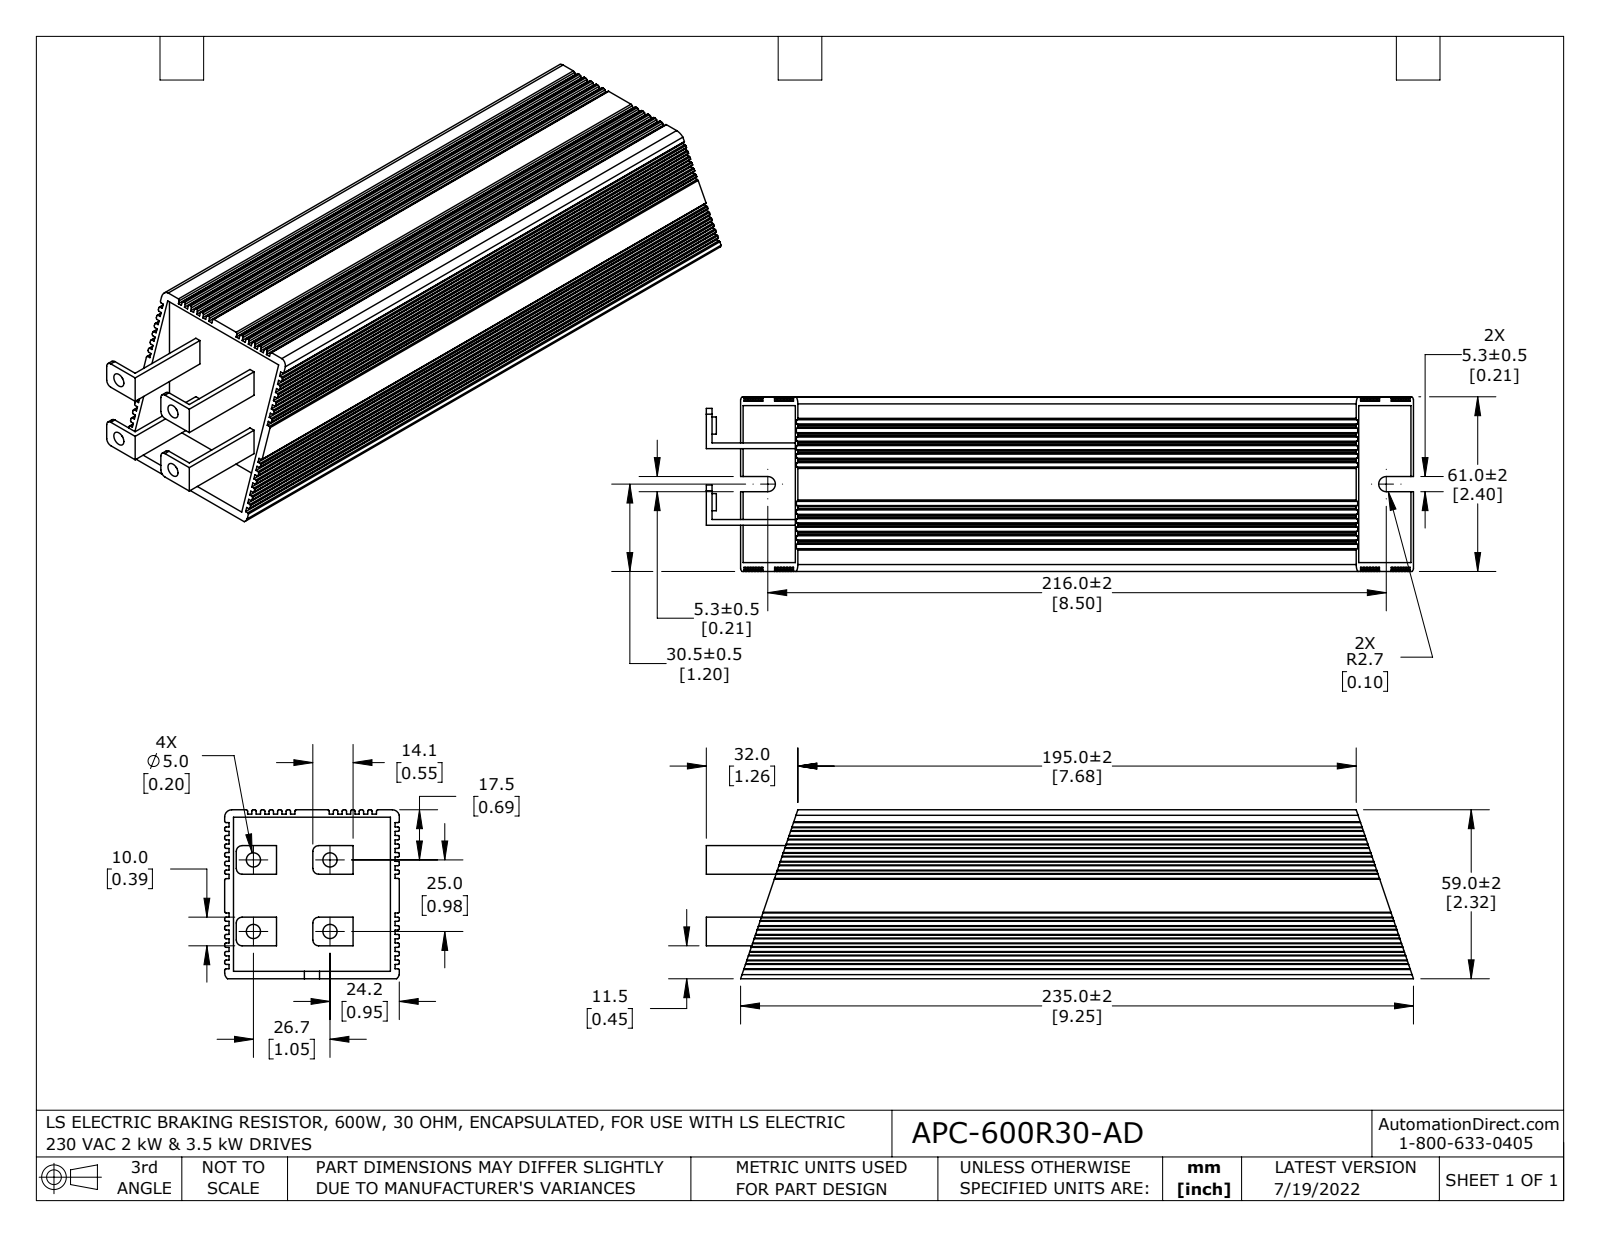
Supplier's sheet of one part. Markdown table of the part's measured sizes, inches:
| quantity | value |
| --- | --- |
| part name | APCS-600R140-AD |
| STEP written by | SolidWorks 2021 (AUTOMOTIVE_DESIGN) |
| units | inches |
| bodies | 1 solid, 322 faces (212 planar, 18 cylindrical, 92 other) |
| overall size | 9.723 × 2.401 × 2.323 |
| volume | 42.56 in³ |
| surface area | 137.2 in² |
| round holes (diameter × count) | 0.196 × 4 |
| round bosses / shafts (diameter × count) | 0.236 × 4 |
| partial cylindrical surfaces (radius × count) | 0.104 × 2 |
| main face-to-face distances | 0.06, 2.323, 0.06, 2.341, 2.283, 0.058, 2.343, 2.401, 0.117, 2.263 |
| hole center spacings | 0.983, 1.053, 1.441 |
